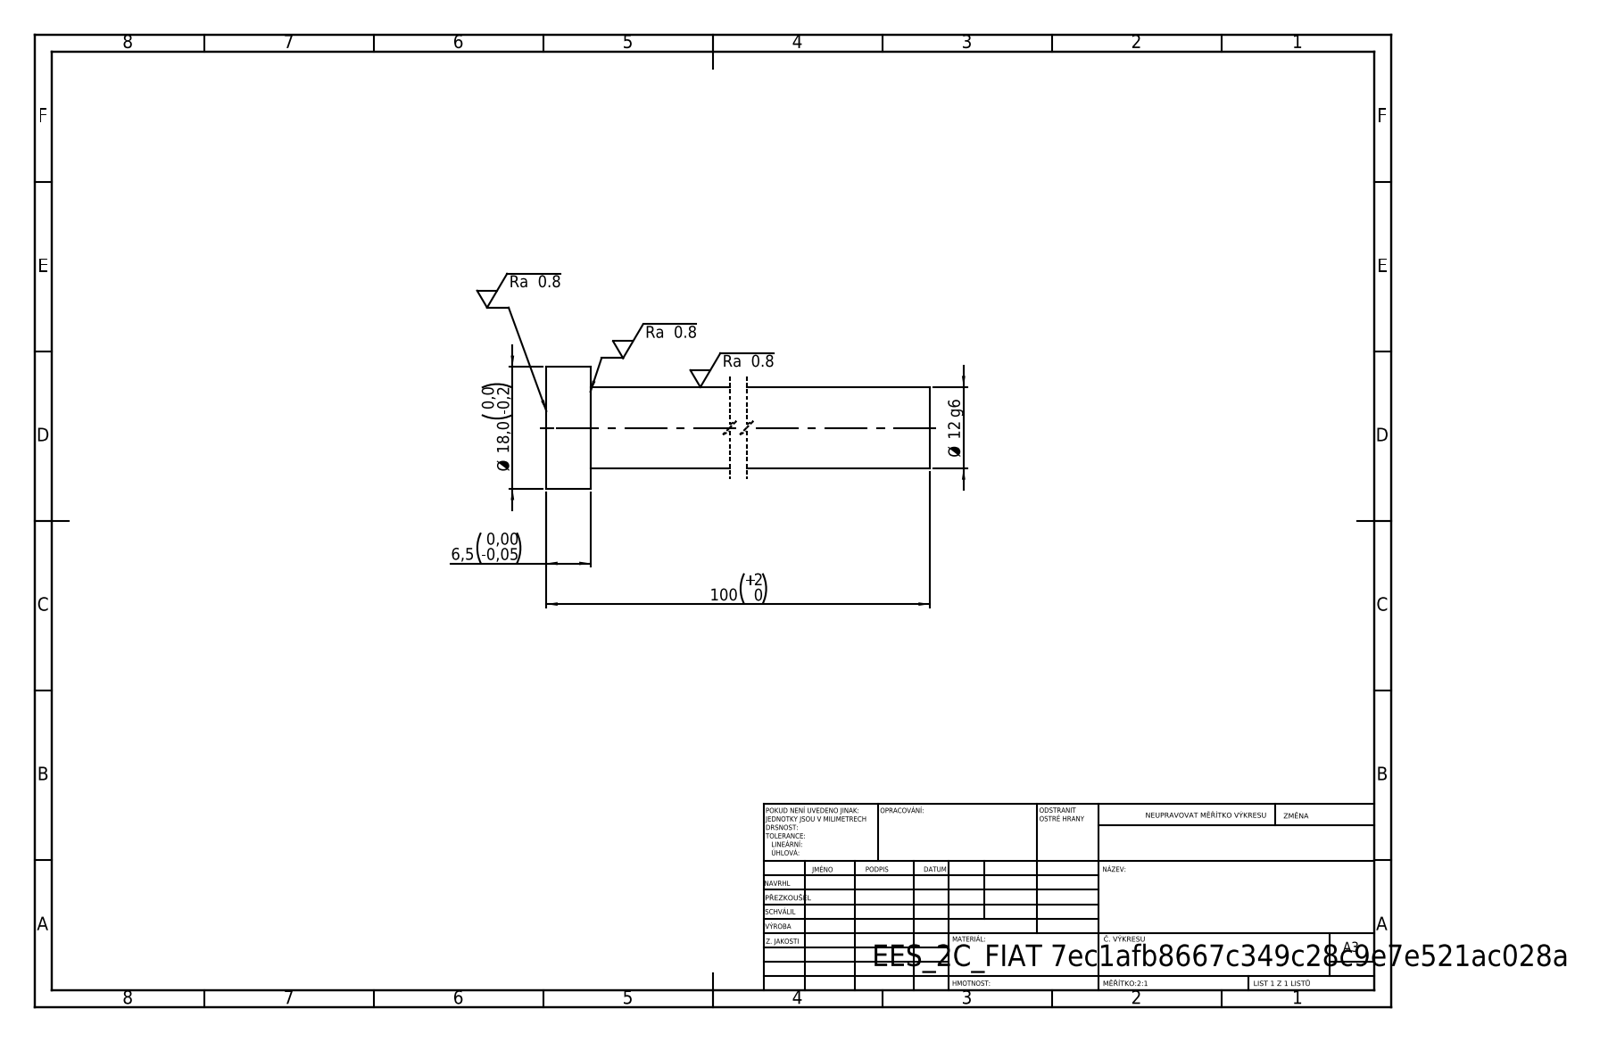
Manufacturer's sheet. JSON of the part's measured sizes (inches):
{"step_written_by": "SolidWorks 2019 (CONFIG_CONTROL_DESIGN)", "units": "inches", "bodies": {"solids": 1, "faces": 7, "planar": 3, "cylindrical": 4, "other": 0}, "overall_size": [3.937, 0.709, 0.709], "volume_in3": 0.746, "surface_area_in2": 6.822, "round_bosses_or_shafts": [[0.709, 1], [0.472, 1]], "face_to_face_distances": [0.256, 3.937, 3.681]}
